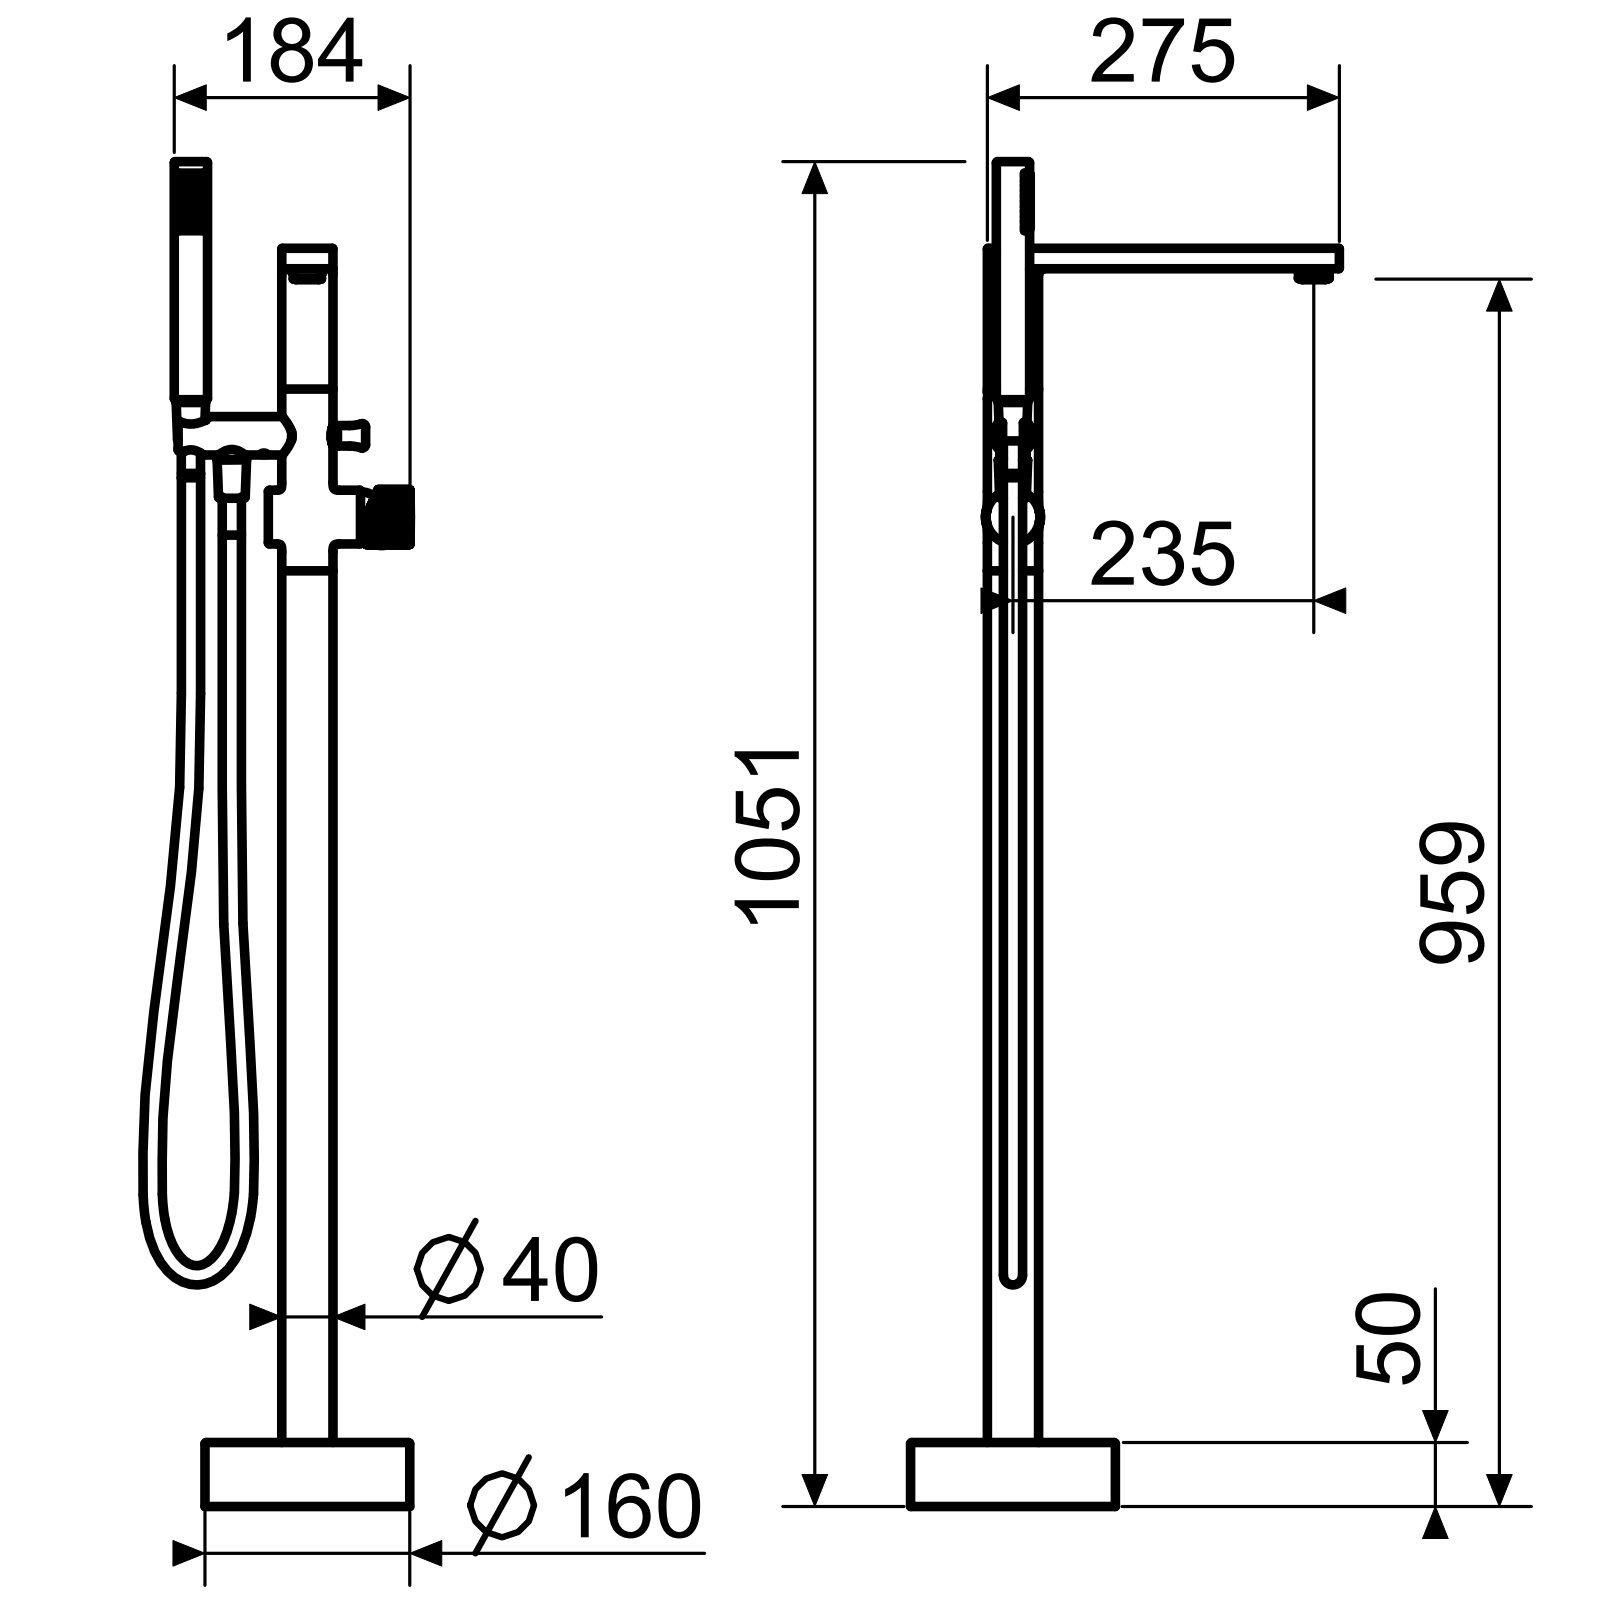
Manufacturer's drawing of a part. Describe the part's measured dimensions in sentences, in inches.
The part is named "TOM3F6418CCS8NY_9; TOM3F6418CCS8NY_30; TOM3F6418CCS8NY_15; ALOG005C007 (+8 more)". Its 3-D file was written by "CREO PARAMETRIC BY PTC INC, 2022164 (CONFIG_CONTROL_DESIGN)". It is 18 solids with 6632 faces: 2585 planar, 1740 cylindrical and 2307 other. Overall it measures 41.366 by 13.189 by 8.225 inches. Its volume is 51.74 cubic inches and its surface area 802.2 square inches. Round holes: 44 of diameter 0.024, 30 of diameter 0.02, 7 of diameter 0.276, 5 of diameter 0.433, 4 of diameter 0.165, 4 of diameter 0.669, 3 of diameter 0.256, 3 of diameter 0.748, 2 of diameter 0.217, 2 of diameter 0.236, 2 of diameter 0.315, 2 of diameter 0.394. Round bosses or shafts: 75 of diameter 0.059, 3 of diameter 0.63, 2 of diameter 0.827, 2 of diameter 0.724, 2 of diameter 0.551, 1 of diameter 6.299, 1 of diameter 1.654, 1 of diameter 1.575. Partial cylindrical surfaces (rounded edges, fillets, slot ends): 8 of radius 0.02, 2 of radius 0.012, 2 of radius 0.098, 1 of radius 0.163, 1 of radius 0.54, 1 of radius 0.551, 1 of radius 0.701, 1 of radius 0.787. The main face-to-face distances are 0.087, 0.039, 0.543, 36.772, 36.732, 36.685, 36.646, 0.63, 36.142, 36.102. The hole center spacings are 0.142, 0.264, 0.411, 0.157, 0.315, 0.564, 0.719, 0.472.
